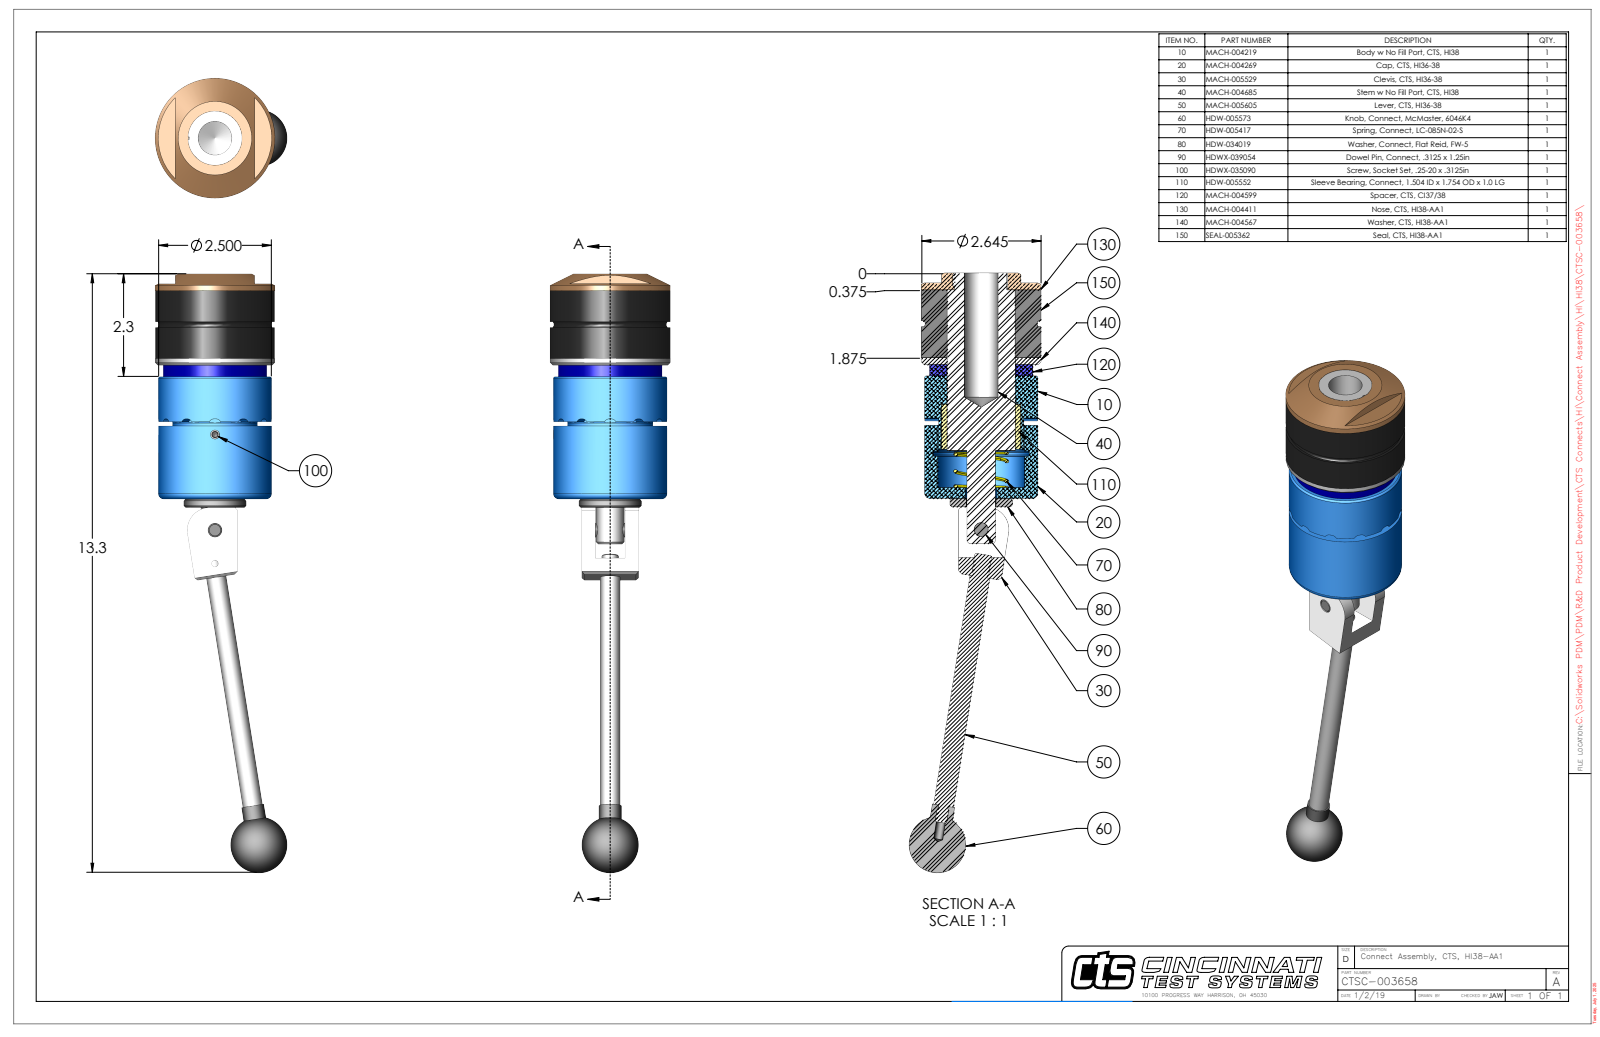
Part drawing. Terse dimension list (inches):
name: CTSC-003658
written by: SolidWorks 2023 (AUTOMOTIVE_DESIGN)
unit: in
bodies: 10 solids, 275 faces (98 planar, 108 cylindrical, 69 other)
size: 13.275 × 2.915 × 2.645
volume: 26.94 in³; area: 143.1 in²
holes: 2× ⌀0.201, 1× ⌀0.15, 1× ⌀0.311, 1× ⌀0.313, 1× ⌀0.314, 1× ⌀0.656, 1× ⌀0.696, 1× ⌀0.75, 1× ⌀1.172, 1× ⌀1.495, 1× ⌀1.501, 1× ⌀1.51
bosses: 1× ⌀2.645, 1× ⌀2.645, 1× ⌀2.5, 1× ⌀2.281, 1× ⌀1.875, 1× ⌀1.5, 1× ⌀1.496, 1× ⌀1.38
rounds: 12× R0.12, 2× R0.029, 1× R0.5, 1× R1.206
face distances: 1.5, 0.152, 1.652, 0.25, 0.402, 1.902, 2.713, 2.963, 3.115, 4.615
hole spacings: 0.74, 2.118, 2.858
